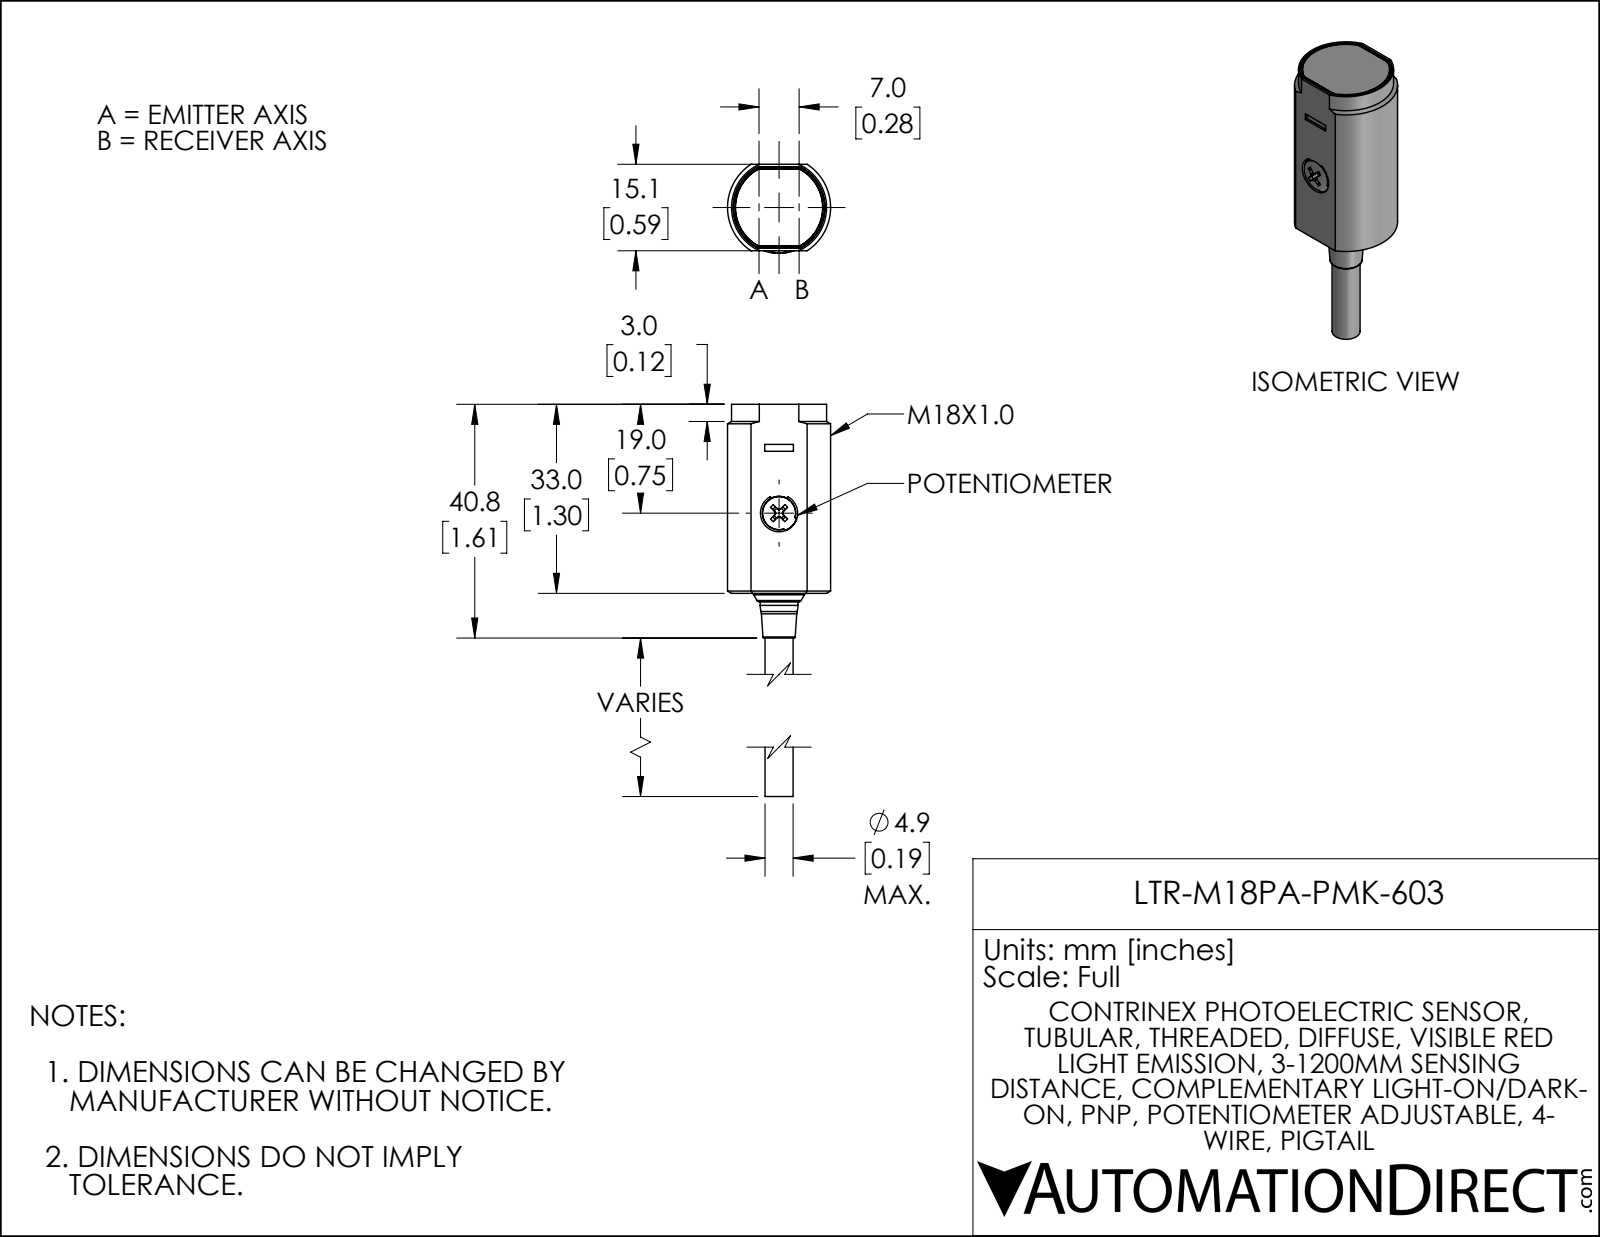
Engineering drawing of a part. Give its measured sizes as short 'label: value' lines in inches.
name: LTR-M18PA-PMK-603
written by: SolidWorks 2021 (AUTOMOTIVE_DESIGN)
unit: in
bodies: 1 solid, 116 faces (58 planar, 40 cylindrical, 18 other)
size: 2.205 × 0.709 × 0.611
volume: 0.5 in³; area: 4.262 in²
holes: 1× ⌀0.256
bosses: 1× ⌀0.26, 1× ⌀0.193
rounds: 8× R0.014, 8× R0.028, 4× R0.006, 4× R0.024, 1× R0.116, 1× R0.299, 1× R0.302, 1× R0.313
face distances: 0.594, 1.297, 0.016, 1.299, 2.205, 2.203, 0.906, 0.579, 0.563, 0.014
